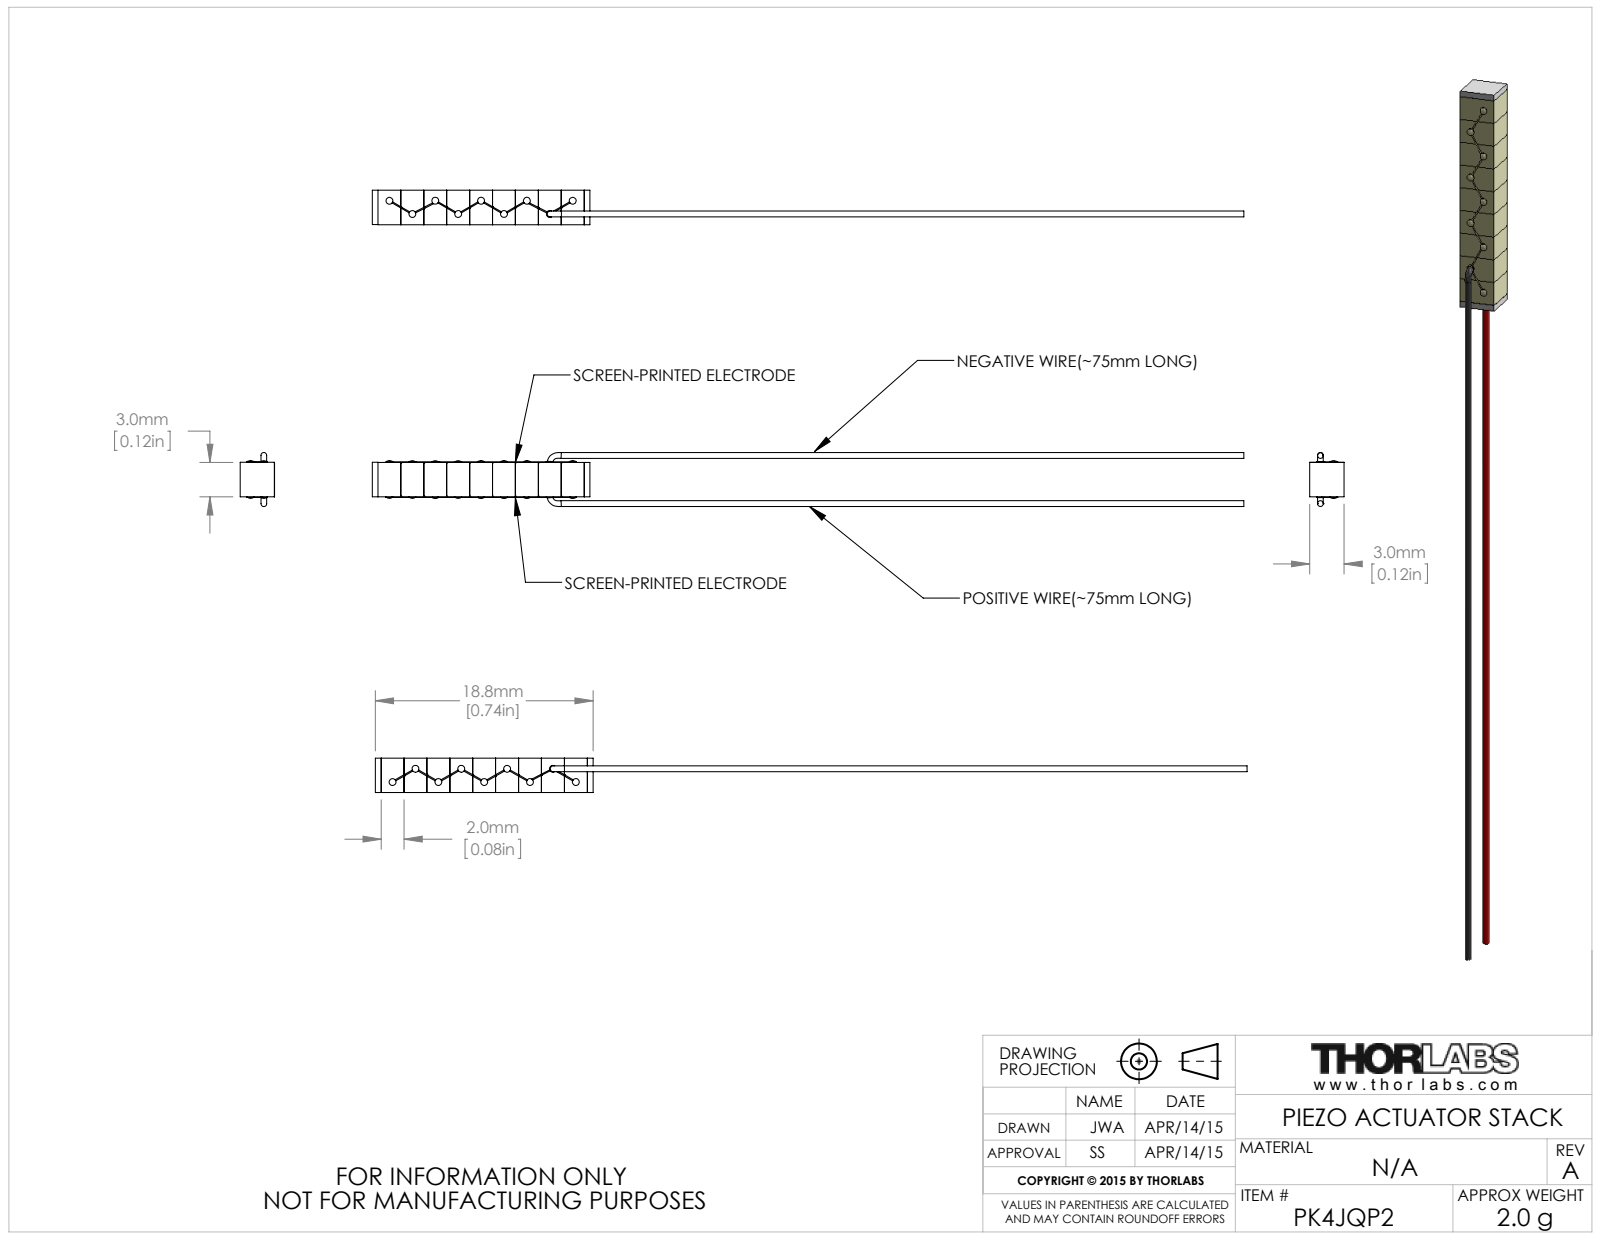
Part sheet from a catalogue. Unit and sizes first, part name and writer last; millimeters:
Units: millimetres
Overall size (bounding box): 76.1 × 4.72 × 3
Round bosses / shafts (diameter × count): ⌀0.6 ×9
Main face-to-face distances: 2, 4, 6, 3, 8, 10, 12, 14, 16, 0.5
Volume: 196 mm³ · Surface area: 622 mm²
Bodies: 3 solids, 203 faces (82 planar, 83 cylindrical, 38 other)
Part name (STEP PRODUCT): CTN002958
STEP written by: SolidWorks 2014 (AUTOMOTIVE_DESIGN)
